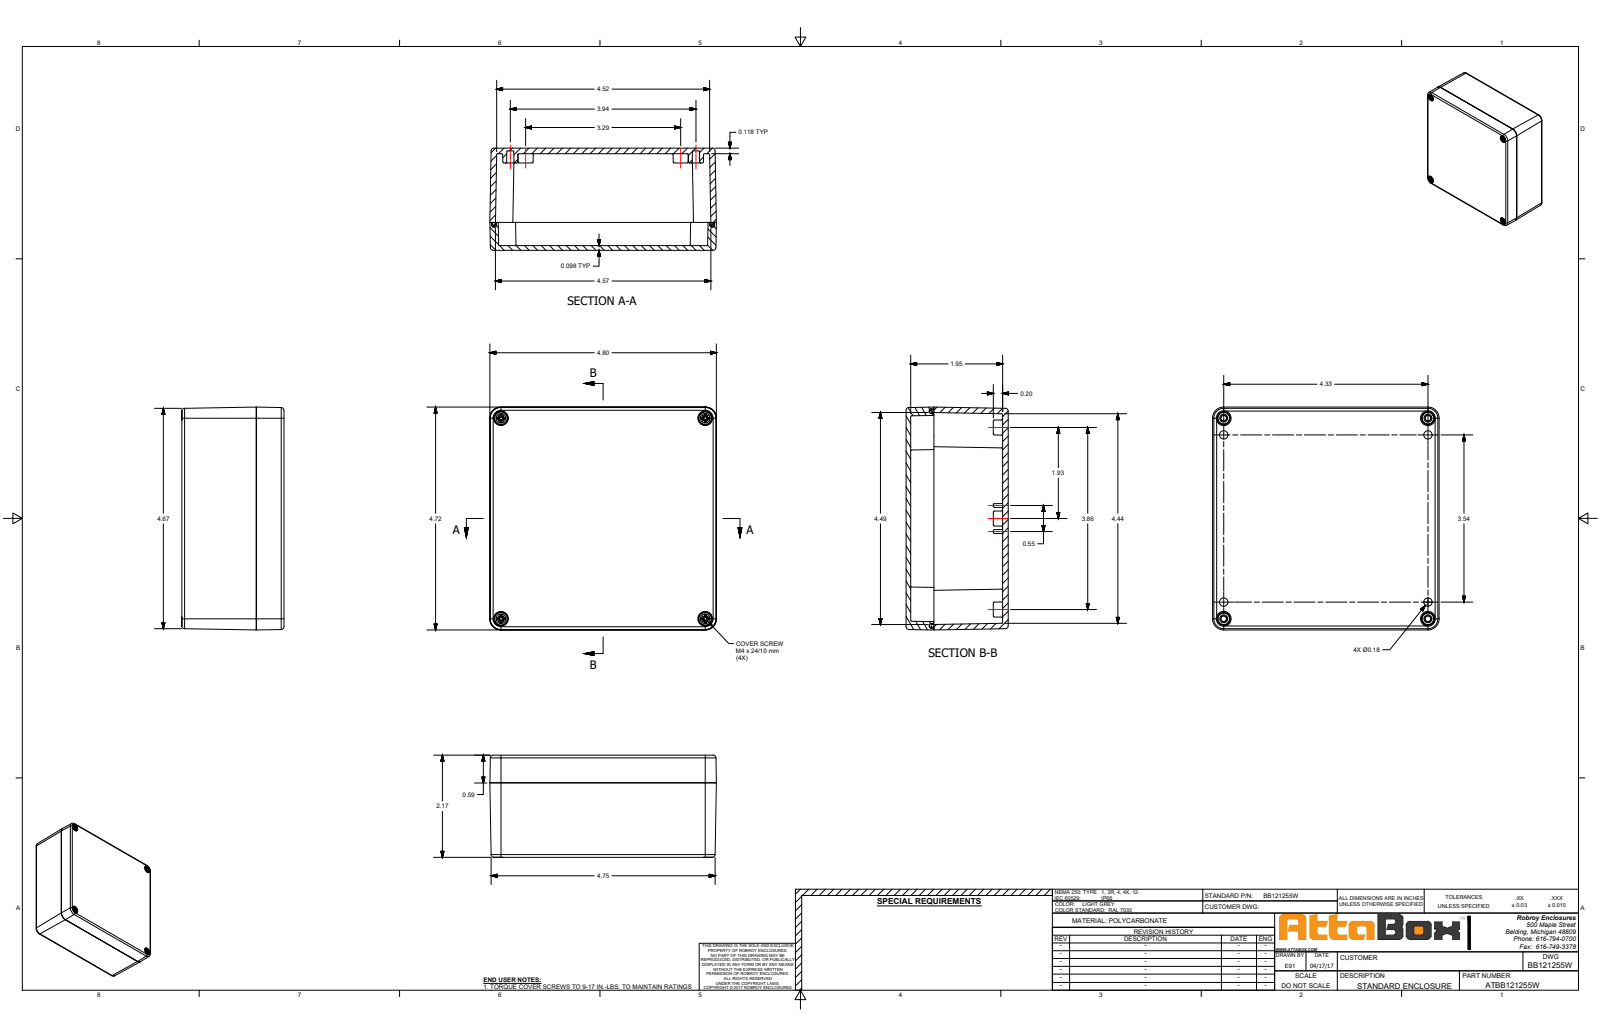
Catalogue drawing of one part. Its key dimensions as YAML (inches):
part_name: "BB121255W"
step_written_by: "SolidWorks 2018 (AUTOMOTIVE_DESIGN)"
units: inches
bodies: {solids: 11, faces: 1793, planar: 611, cylindrical: 492, other: 690}
overall_size: [4.803, 4.724, 2.167]
volume: 10.47
surface_area: 195.8
round_holes:
  - {diameter: 0.177, count: 8}
  - {diameter: 0.128, count: 4}
  - {diameter: 0.189, count: 4}
  - {diameter: 0.201, count: 4}
  - {diameter: 0.276, count: 4}
  - {diameter: 0.295, count: 4}
  - {diameter: 0.315, count: 4}
round_bosses_or_shafts:
  - {diameter: 0.268, count: 4}
  - {diameter: 0.173, count: 4}
  - {diameter: 0.157, count: 4}
  - {diameter: 0.13, count: 4}
partial_cylinders:
  - {radius: 0.039, count: 48}
  - {radius: 0.02, count: 40}
  - {radius: 0.008, count: 32}
  - {radius: 0.197, count: 12}
  - {radius: 0.059, count: 8}
  - {radius: 0.098, count: 8}
  - {radius: 0.102, count: 4}
  - {radius: 0.118, count: 4}
face_to_face_distances: [0.118, 2.165, 0.098, 2.067, 2.047, 1.949, 0.116, 0.177, 4.724, 4.685]
hole_center_spacings: [0.354, 3.898, 4.331, 4.345, 5.826, 3.543, 4.252, 5.596]
